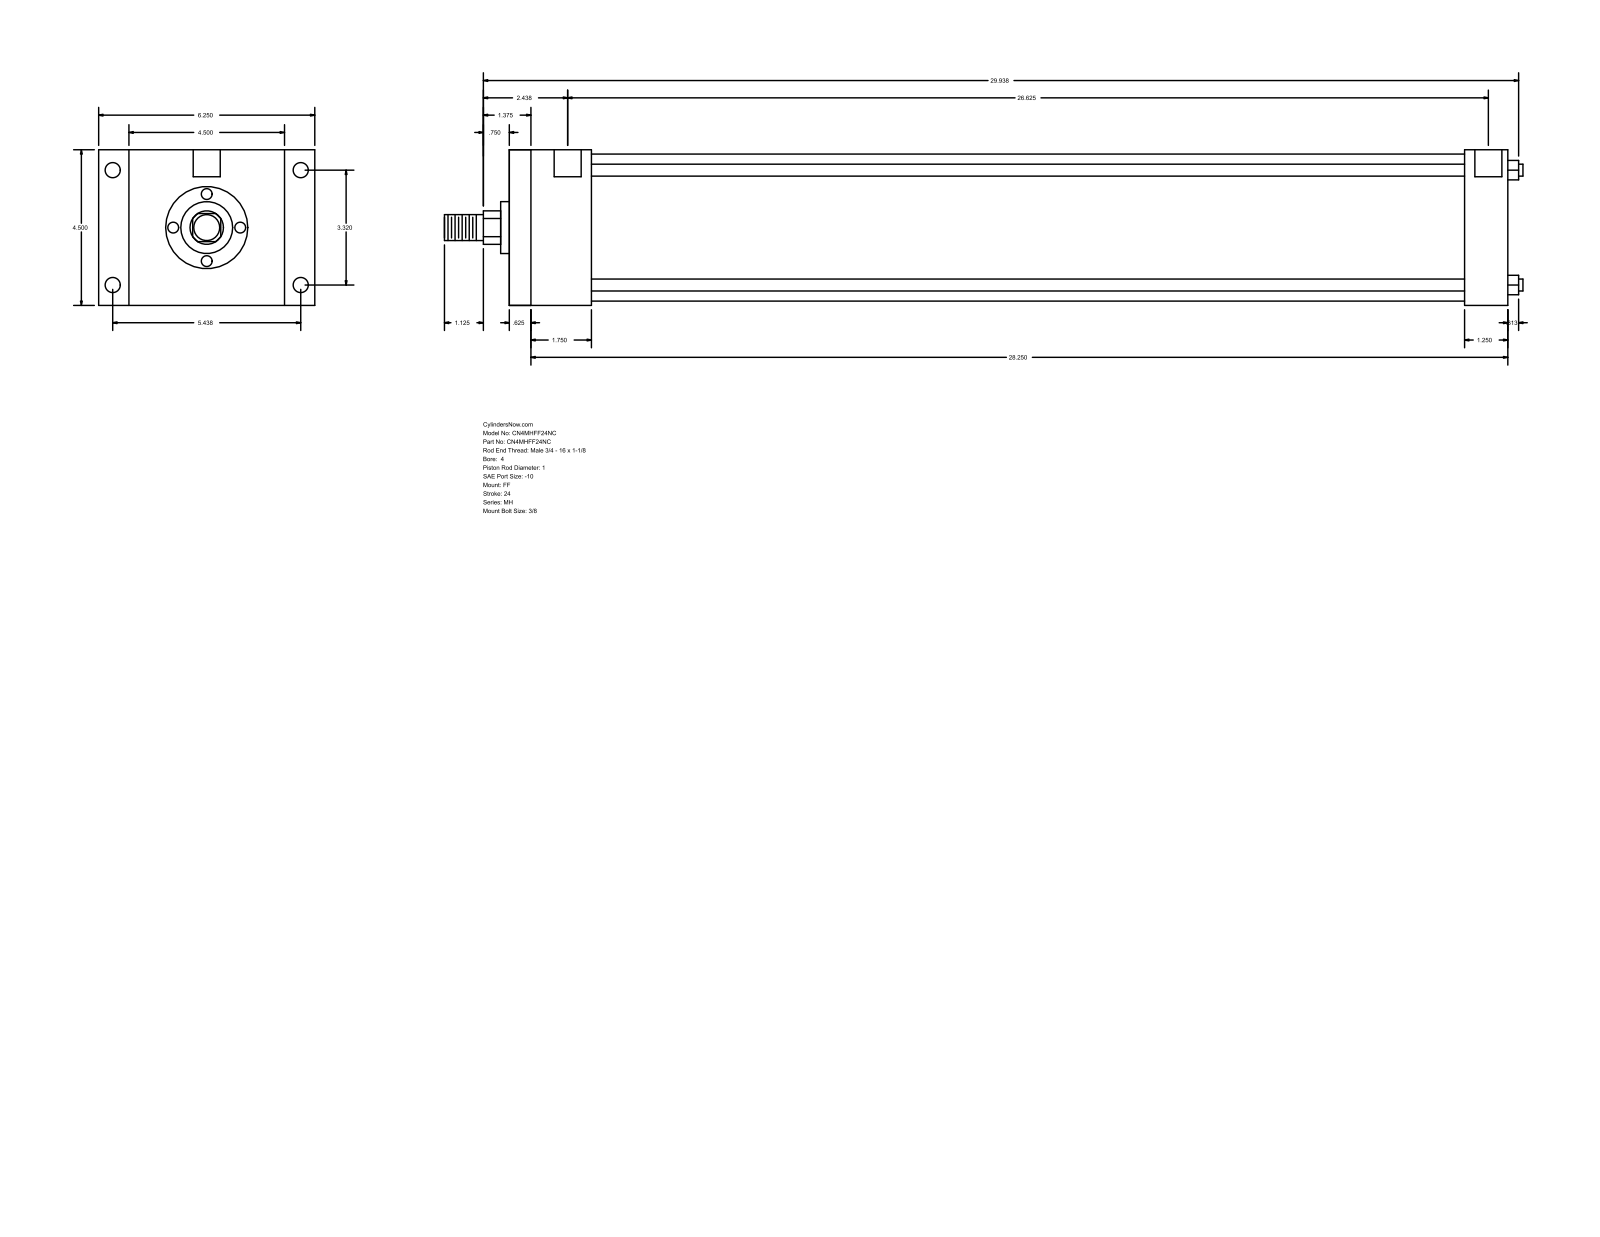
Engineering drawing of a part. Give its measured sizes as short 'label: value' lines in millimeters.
name: MH_FF__0400_1
written by: GSSL Pune (CONFIG_CONTROL_DESIGN)
unit: mm
bodies: 0 solids, 92 faces (64 planar, 28 cylindrical, 0 other)
size: 792.16 × 158.75 × 114.3
holes: 4× ⌀8.73, 4× ⌀11.13, 2× ⌀19.84
bosses: 4× ⌀8.76, 1× ⌀107.95, 1× ⌀38.1, 1× ⌀25.4, 1× ⌀19.05
rounds: 1× R12.29
face distances: 114.3, 733.43, 15.87, 717.56, 60.33, 44.46, 673.1, 701.68, 685.81, 641.35
hole spacings: 1.58, 84.32, 138.12, 161.82, 677.86, 679.44, 676.28
